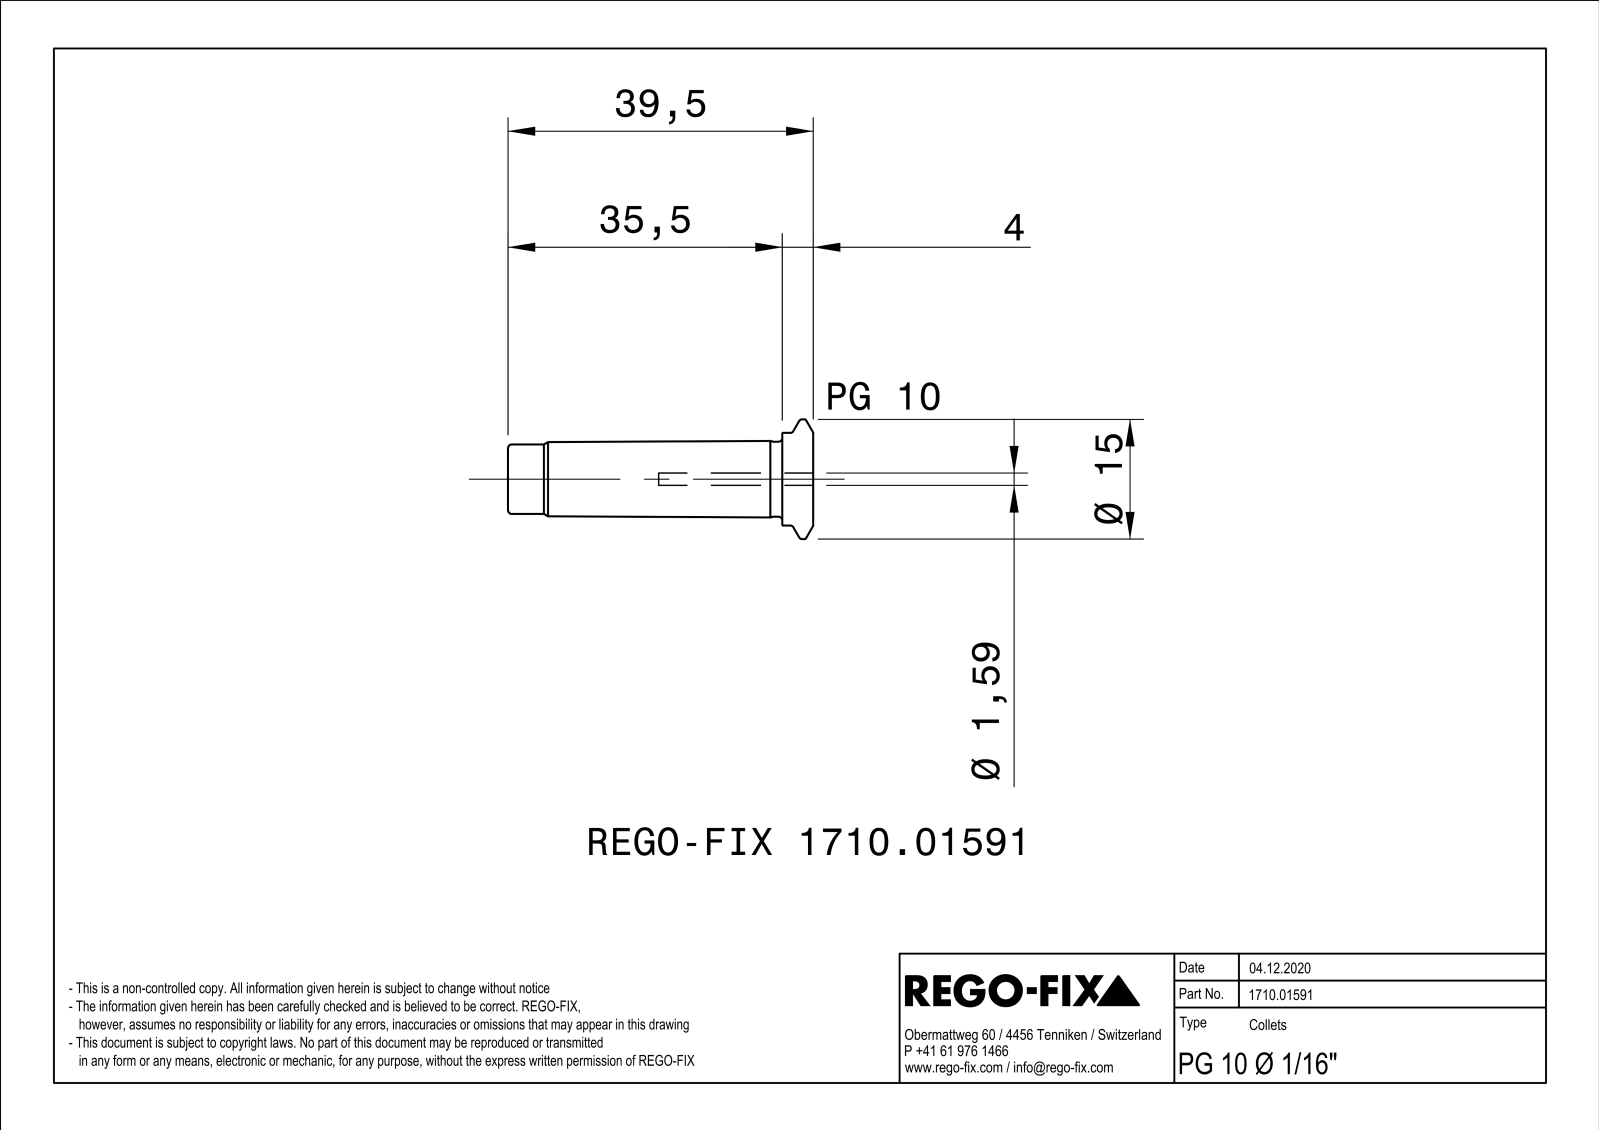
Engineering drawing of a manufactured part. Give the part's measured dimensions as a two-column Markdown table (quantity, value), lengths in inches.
| quantity | value |
| --- | --- |
| part name | NOCUT |
| STEP written by | SIEMENS PLM Software Solid Edge ST10 (AUTOMOTIVE_DESIGN) |
| units | inches |
| bodies | 1 solid, 63 faces (11 planar, 13 cylindrical, 39 other) |
| overall size | 1.555 × 0.61 × 0.61 |
| volume | 0.155 in³ |
| surface area | 3.808 in² |
| round holes (diameter × count) | 0.063 × 1, 0.244 × 1 |
| round bosses / shafts (diameter × count) | 0.61 × 1, 0.472 × 1, 0.382 × 1, 0.354 × 1 |
| main face-to-face distances | 0.031, 1.555, 0.157, 1.398 |
